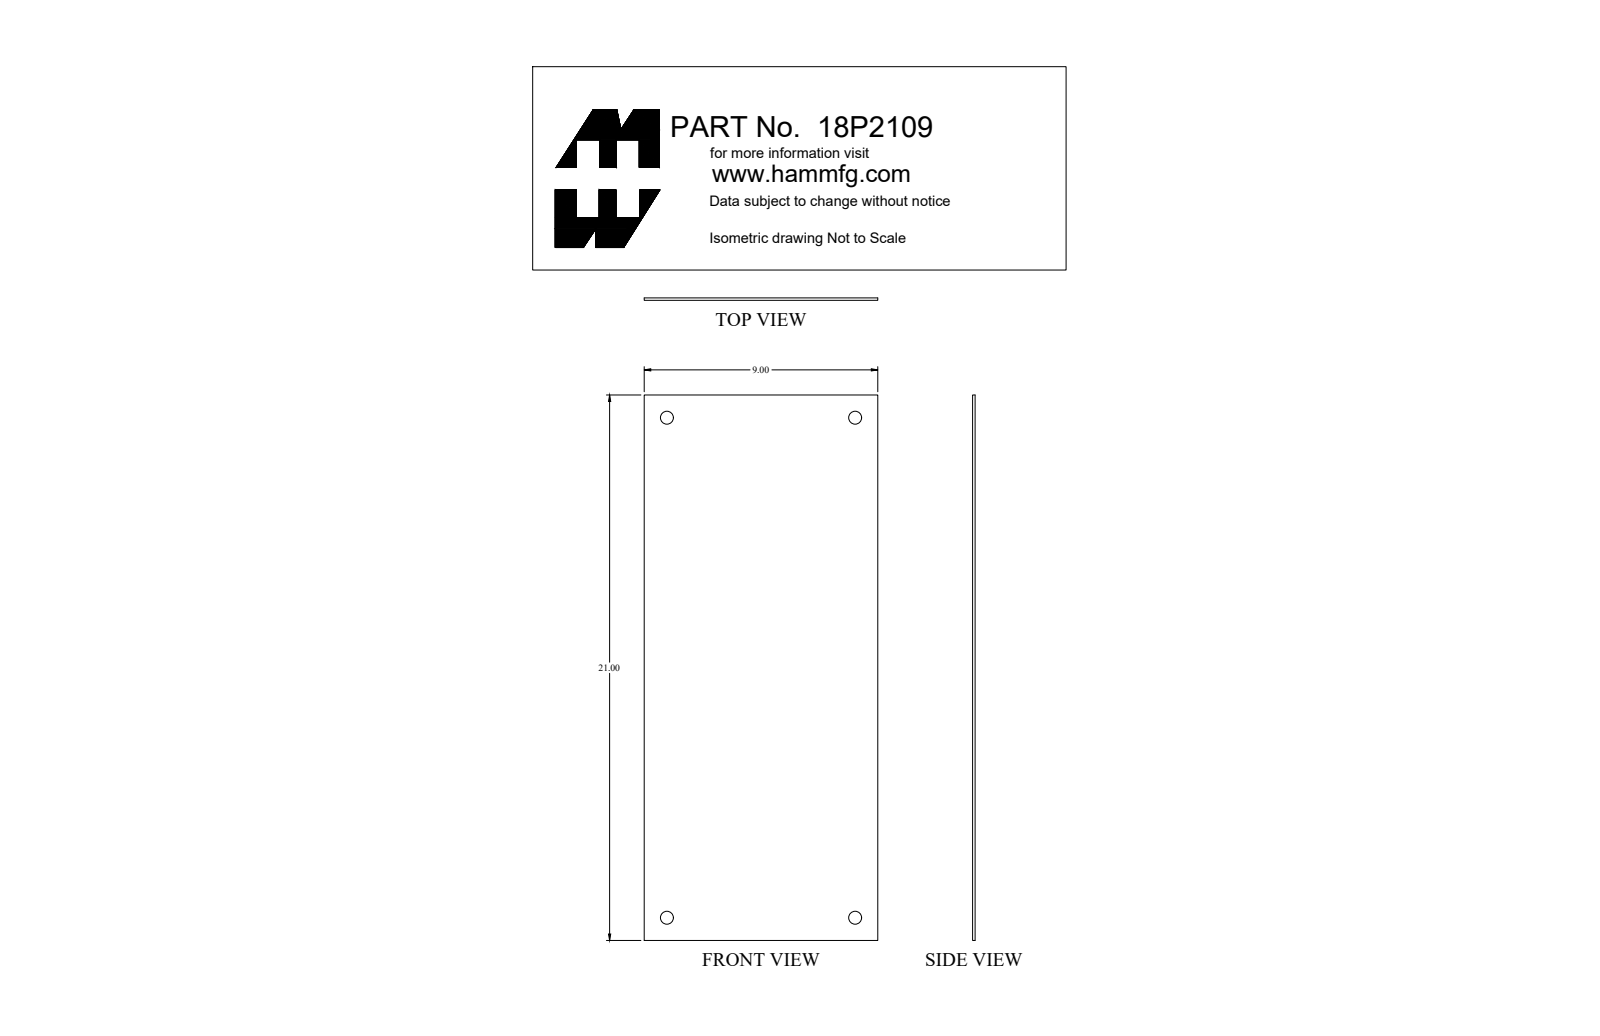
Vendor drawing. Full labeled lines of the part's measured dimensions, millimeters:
Part name (STEP PRODUCT): 18P2109_Default
STEP written by: SolidWorks 2018 (CONFIG_CONTROL_DESIGN)
Units: millimetres
Bodies: 1 solid, 14 faces (6 planar, 8 cylindrical, 0 other)
Overall size (bounding box): 533.4 × 228.6 × 2.4
Volume: 293 000 mm³ · Surface area: 246 900 mm²
Round holes (diameter × count): ⌀12.7 ×4
Main face-to-face distances: 2.4, 228.6, 533.4
Hole centre spacings: 184.2, 489, 522.5
